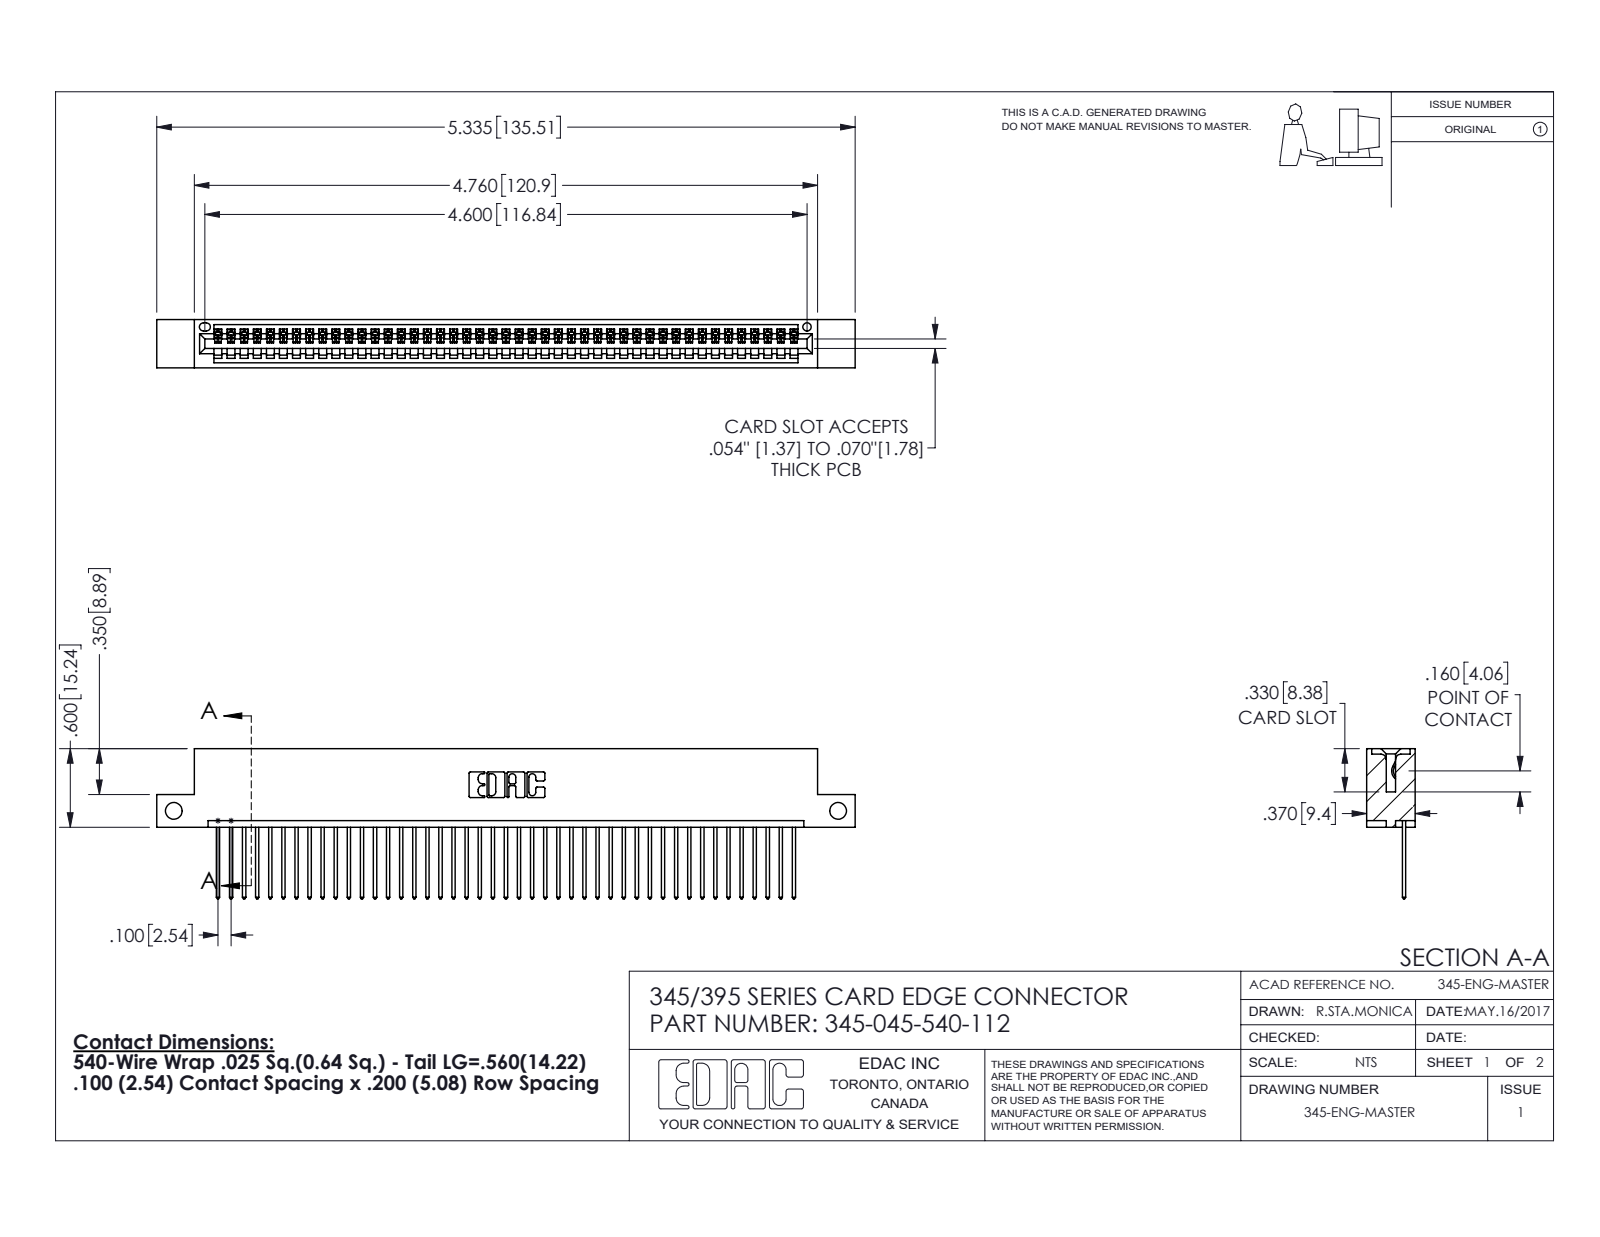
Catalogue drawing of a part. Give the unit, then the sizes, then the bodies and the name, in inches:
Units: inches
Overall size (bounding box): 5.335 × 1.147 × 0.37
Round holes (diameter × count): ⌀0.128 ×2, ⌀0.064 ×1
Partial cylindrical surfaces — rounded edges, fillets, slot ends (radius × count): R0.006 ×90, R0.01 ×90, R0.01 ×22, R0.007 ×6, R0.031 ×6, R0.026 ×3, R0.031 ×2, R0.04 ×2
Main face-to-face distances: 0.298, 0.072, 0.37, 0.2, 0.098, 0.272, 0.025, 0.225, 0.149, 0.072
Hole centre spacings: 5.075
Volume: 0.785 in³ · Surface area: 27.03 in²
Bodies: 46 solids, 2736 faces (1880 planar, 856 cylindrical, 0 other)
Part name (STEP PRODUCT): 345 Part_Flush Mounting Lugs - Side Mount; 345-292-001_345-293-140; 345-045-540-112
STEP written by: SolidWorks 2016 (CONFIG_CONTROL_DESIGN)
